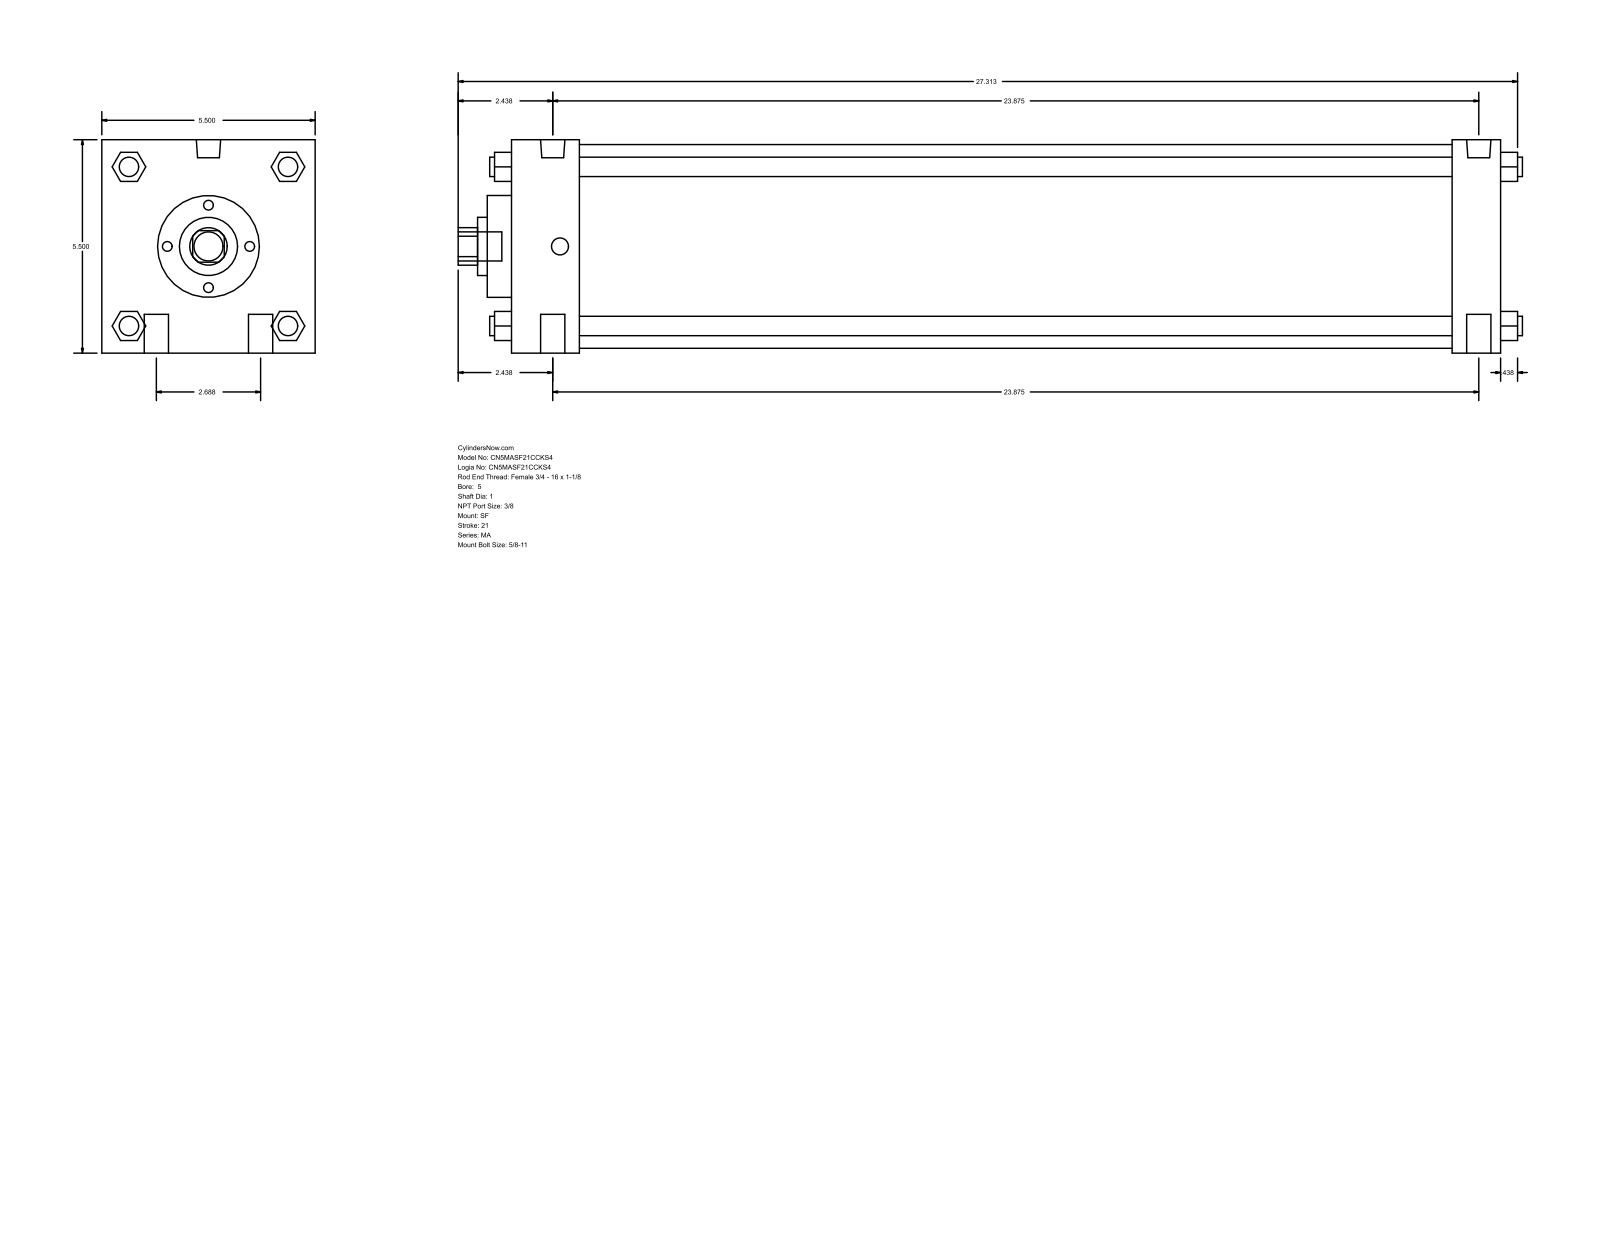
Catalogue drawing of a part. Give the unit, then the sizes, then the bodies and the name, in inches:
Units: inches
Overall size (bounding box): 27.437 × 5.5 × 5.5
Round holes (diameter × count): ⌀1 ×1, ⌀1.5 ×1, ⌀2.625 ×1, ⌀5.25 ×1
Round bosses / shafts (diameter × count): ⌀0.625 ×4, ⌀0.5 ×4, ⌀0.627 ×2, ⌀0.437 ×2, ⌀0.75 ×1
Partial cylindrical surfaces — rounded edges, fillets, slot ends (radius × count): R0.484 ×1
Main face-to-face distances: 5.5, 25.5, 1.75, 24.25, 22.5, 23.75, 1.25, 0.625, 2.375, 24.875
Bodies: 0 solids, 126 faces (95 planar, 31 cylindrical, 0 other)
Part name (STEP PRODUCT): MA_SF__0500_1
STEP written by: GSSL Pune (CONFIG_CONTROL_DESIGN)
